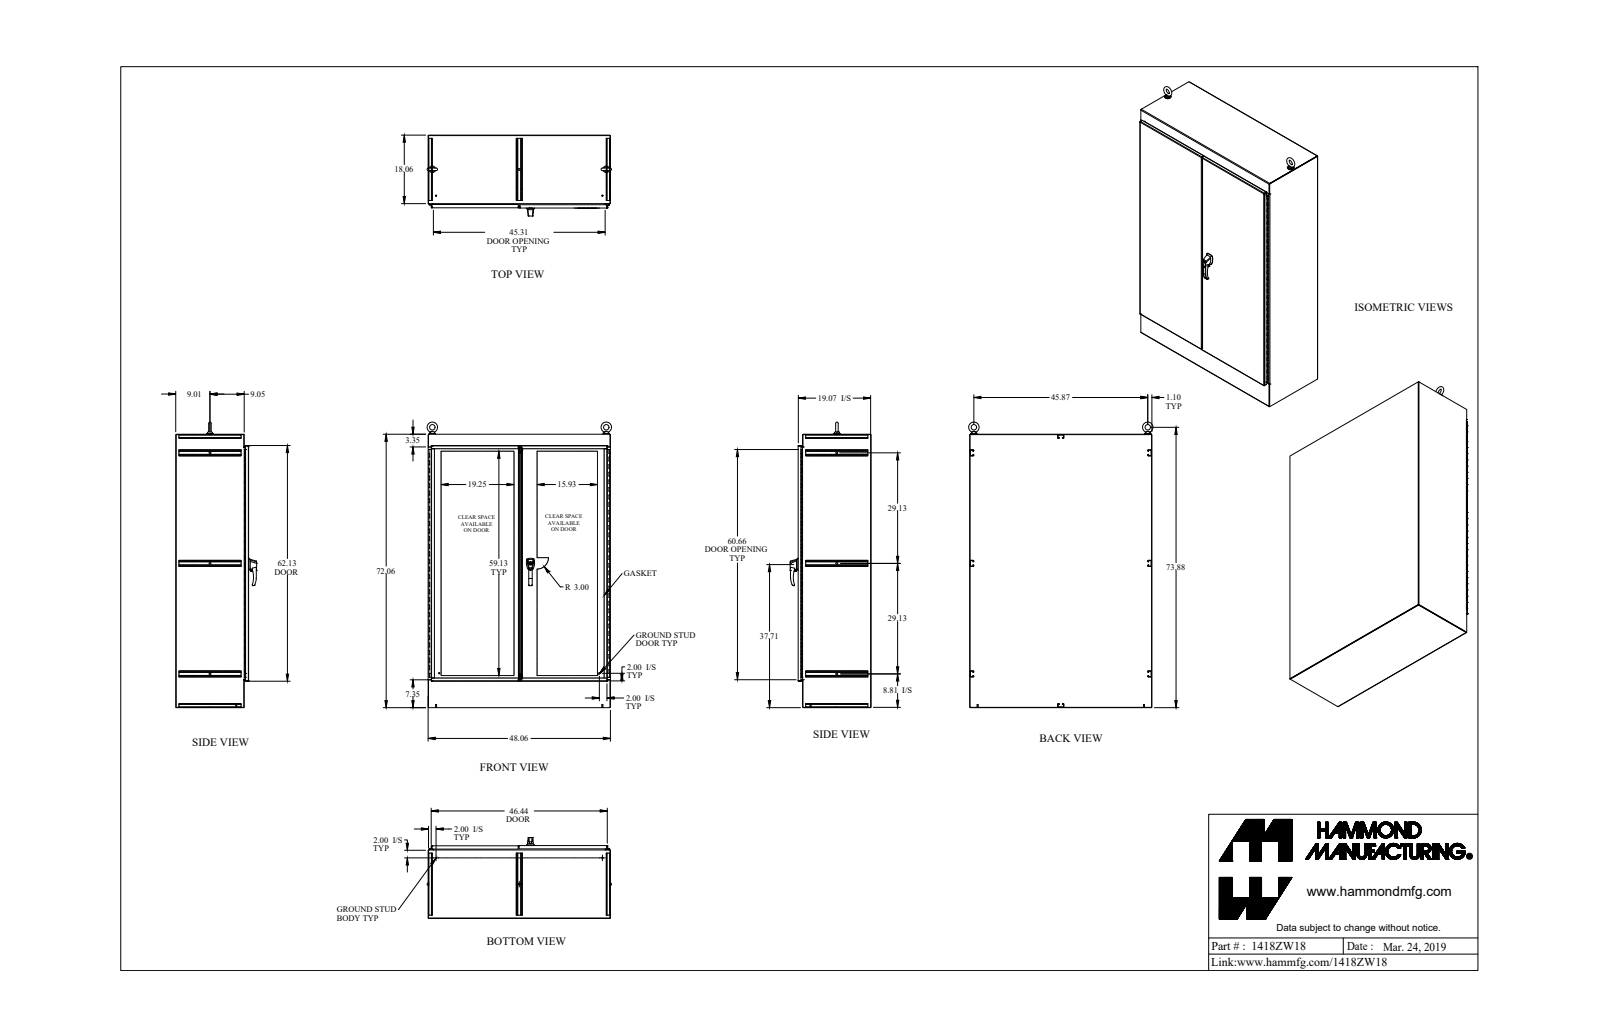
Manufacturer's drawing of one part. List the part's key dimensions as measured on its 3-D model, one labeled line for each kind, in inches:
Part name (STEP PRODUCT): 1418ZW18_Default
STEP written by: SolidWorks 2019 (CONFIG_CONTROL_DESIGN)
Units: inches
Bodies: 71 solids, 2583 faces (1198 planar, 1220 cylindrical, 165 other)
Overall size (bounding box): 75.713 × 49.119 × 21.337
Volume: 1 414 in³ · Surface area: 27 429 in²
Round holes (diameter × count): ⌀0.304 ×20, ⌀0.5 ×4, ⌀0.11 ×2, ⌀0.25 ×2, ⌀0.257 ×2, ⌀0.28 ×2, ⌀0.281 ×2, ⌀0.313 ×2, ⌀0.39 ×2, ⌀0.413 ×2, ⌀0.527 ×2, ⌀0.625 ×2
Round bosses / shafts (diameter × count): ⌀0.281 ×6, ⌀0.25 ×4, ⌀1.75 ×2, ⌀1.5 ×2, ⌀1.25 ×2, ⌀1 ×2, ⌀0.75 ×2, ⌀0.738 ×2
Partial cylindrical surfaces — rounded edges, fillets, slot ends (radius × count): R0.043 ×54, R0.138 ×48, R0.048 ×22, R0.125 ×22, R0.143 ×22, R0.018 ×16, R0.06 ×10, R0.05 ×8
Main face-to-face distances: 0.095, 0.125, 0.062, 47.965, 71.965, 47.87, 18.94, 19.065, 19.002, 19.127
Hole centre spacings: 6, 46.715, 12, 47.857, 18, 49.702, 24, 52.176
